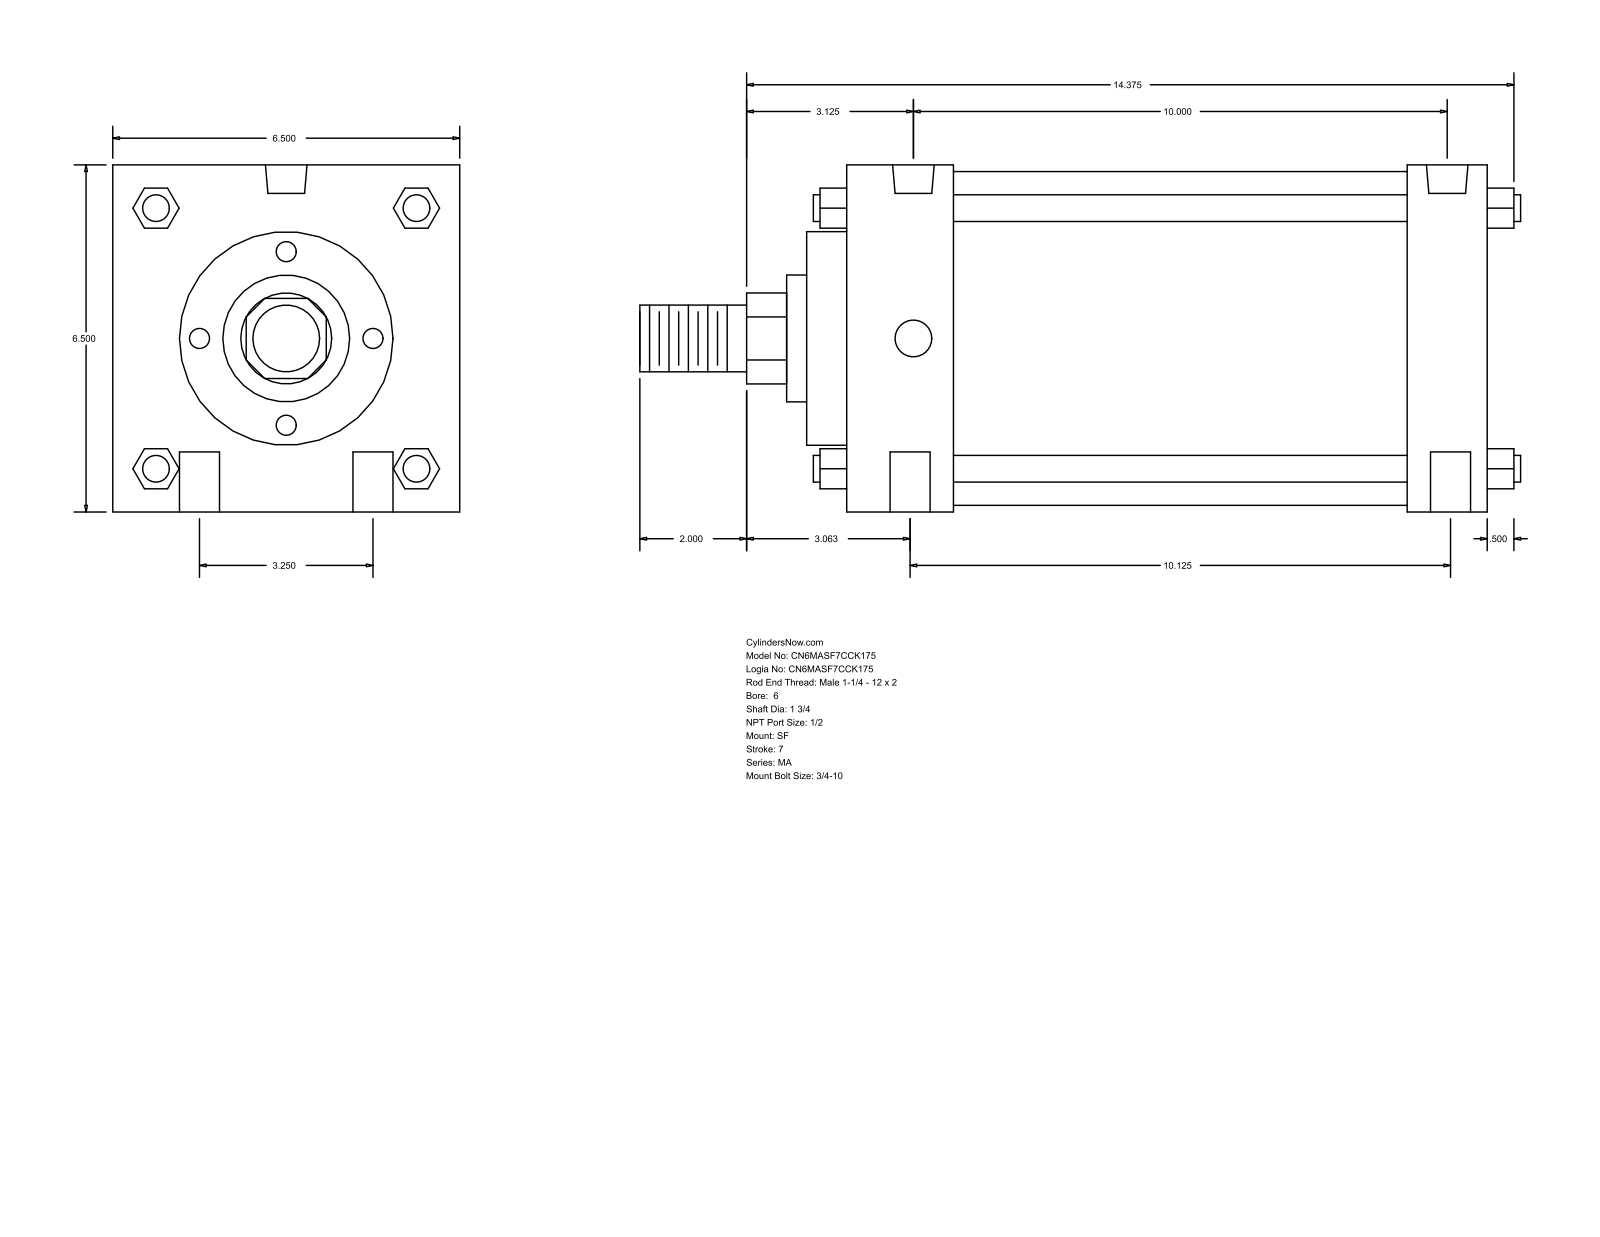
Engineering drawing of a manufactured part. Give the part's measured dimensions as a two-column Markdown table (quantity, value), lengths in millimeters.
| quantity | value |
| --- | --- |
| part name | MA_SF__0600_1.75 |
| STEP written by | GSSL Pune (CONFIG_CONTROL_DESIGN) |
| units | millimeters |
| bodies | 0 solids, 126 faces (95 planar, 31 cylindrical, 0 other) |
| overall size | 419.1 × 165.1 × 165.1 |
| round holes (diameter × count) | 19.05 × 4, 17.46 × 2, 19.77 × 2 |
| round bosses / shafts (diameter × count) | 12.7 × 4, 158.75 × 1, 101.6 × 1, 60.33 × 1, 44.45 × 1, 31.75 × 1 |
| partial cylindrical surfaces (radius × count) | 21.63 × 1 |
| main face-to-face distances | 165.1, 304.81, 19.05, 50.8, 266.7, 38.11, 215.9, 254.01, 69.85, 285.75 |
| hole center spacings | 41.3, 82.54, 254, 257.17, 258.89, 258.9, 270.09 |
